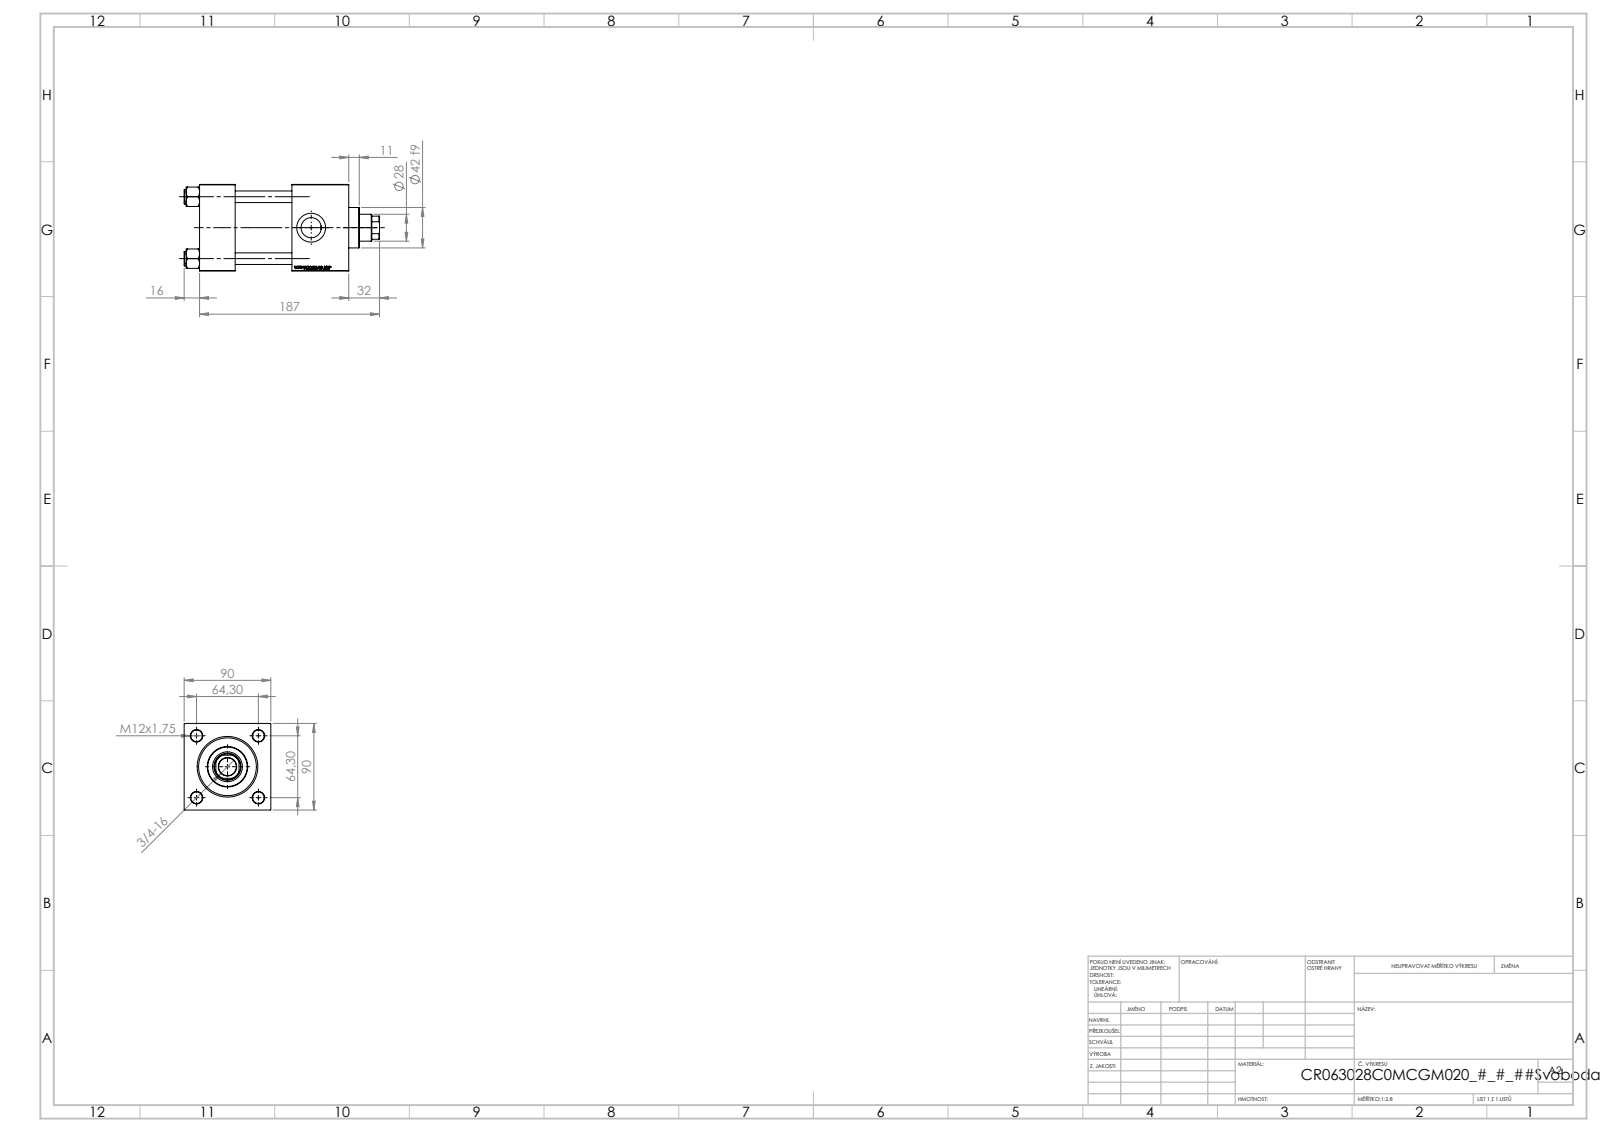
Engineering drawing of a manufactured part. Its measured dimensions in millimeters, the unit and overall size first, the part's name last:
Units: millimetres
Overall size (bounding box): 203 × 90 × 90
Round holes (diameter × count): ⌀12 ×4, ⌀7 ×2, ⌀20.96 ×2, ⌀30 ×2, ⌀18.5 ×1, ⌀28 ×1, ⌀31 ×1, ⌀50 ×1, ⌀60 ×1, ⌀63 ×1
Round bosses / shafts (diameter × count): ⌀15 ×4, ⌀69 ×1, ⌀42 ×1
Partial cylindrical surfaces — rounded edges, fillets, slot ends (radius × count): R13.5 ×1
Main face-to-face distances: 90, 59, 37, 155, 118, 96, 126.3, 89.3, 30.3, 28.7
Hole centre spacings: 45.47, 64.3, 90.93
Volume: 946 794 mm³ · Surface area: 179 129 mm²
Bodies: 11 solids, 1149 faces (526 planar, 87 cylindrical, 536 other)
Part name (STEP PRODUCT): V215_VC_A; V215CR_VCP_C; NUT_M5_C; V215CR_C_TYCINKA (+1 more)
STEP written by: SolidWorks 2019 (CONFIG_CONTROL_DESIGN)
